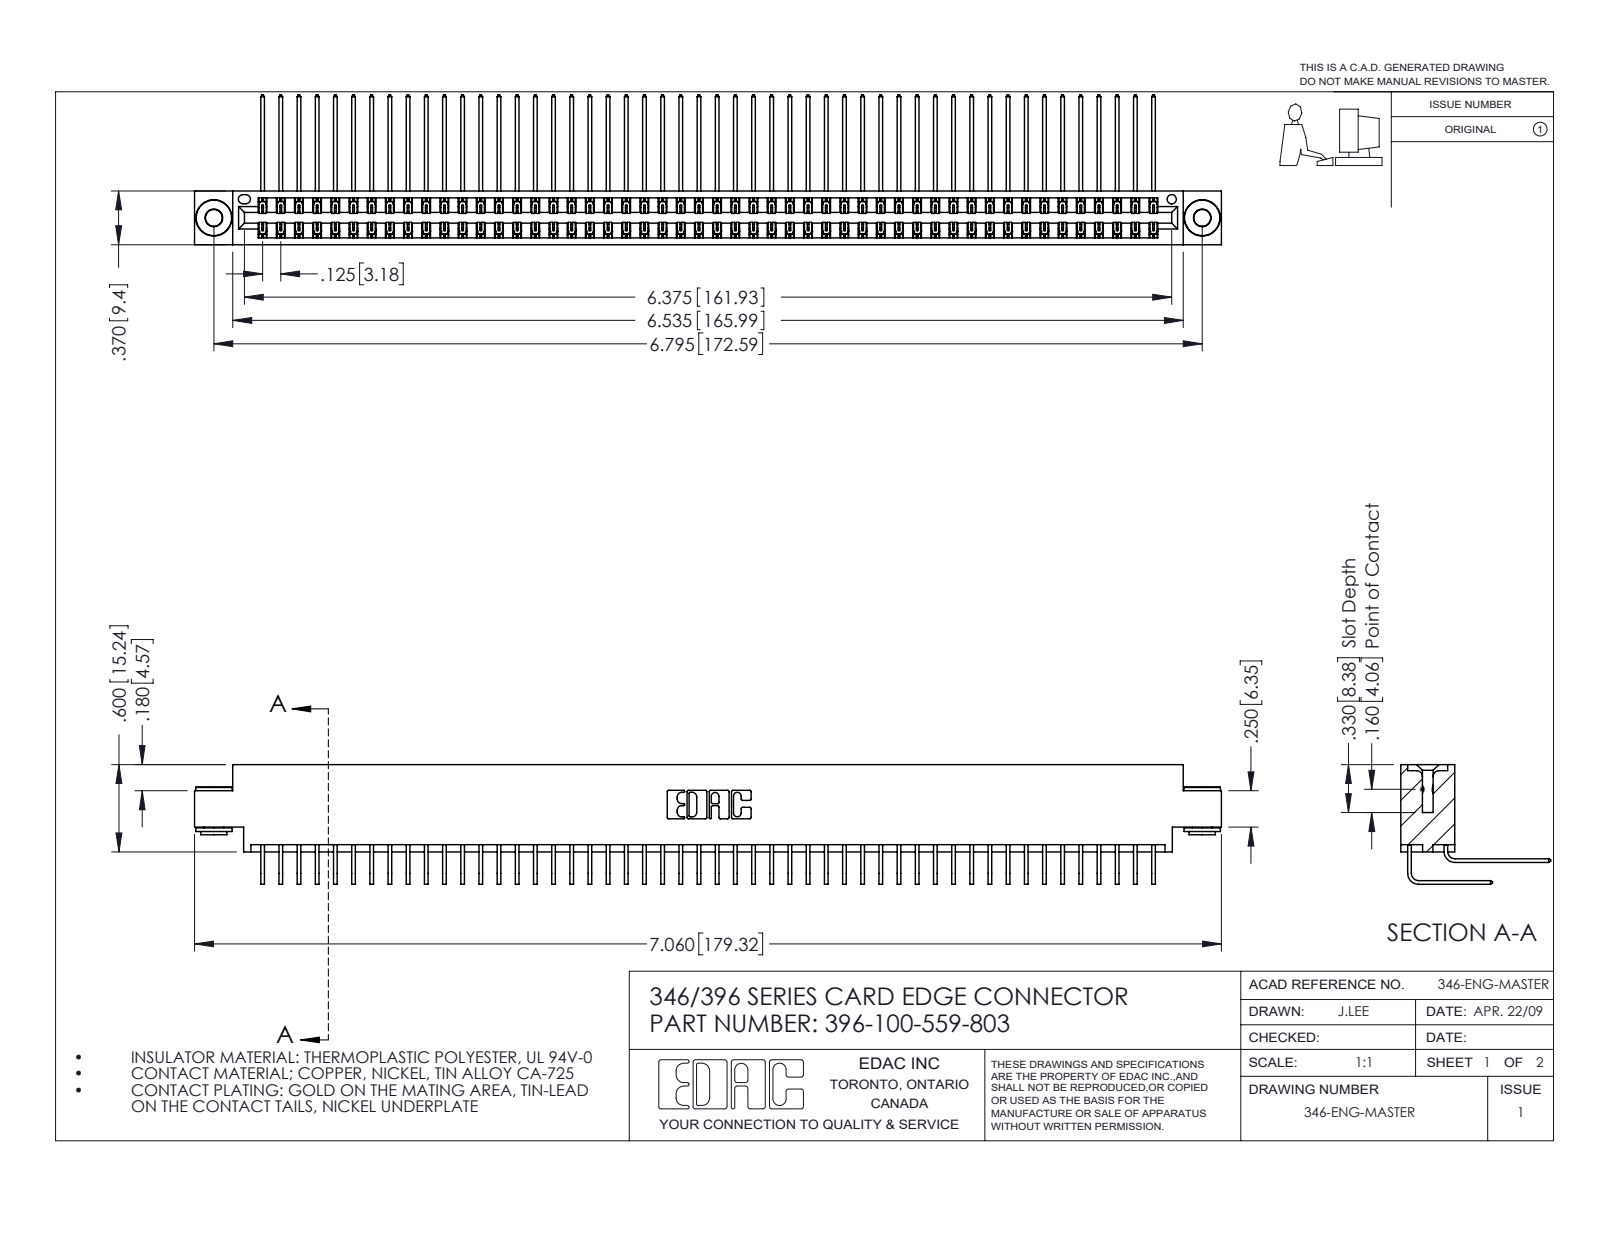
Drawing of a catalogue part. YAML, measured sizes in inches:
part_name: "345-292-001_559 Tail - 2; 396-100-559-803; 345-292-001_558 559 Tail - 1; 345-250-002_345-250-002-102 (+1 more)"
step_written_by: "SolidWorks 2016 (CONFIG_CONTROL_DESIGN)"
units: inches
bodies: {solids: 103, faces: 5564, planar: 3790, cylindrical: 1766, other: 8}
overall_size: [7.06, 1.03, 0.823]
volume: 1.098
surface_area: 43.42
round_holes:
  - {diameter: 0.116, count: 2}
  - {diameter: 0.156, count: 2}
  - {diameter: 0.064, count: 1}
round_bosses_or_shafts:
  - {diameter: 0.25, count: 2}
  - {diameter: 0.18, count: 2}
  - {diameter: 0.136, count: 2}
partial_cylinders:
  - {radius: 0.006, count: 150}
  - {radius: 0.01, count: 22}
  - {radius: 0.007, count: 6}
  - {radius: 0.031, count: 6}
  - {radius: 0.026, count: 3}
  - {radius: 0.014, count: 2}
  - {radius: 0.022, count: 2}
  - {radius: 0.024, count: 2}
face_to_face_distances: [0.048, 0.322, 0.025, 0.37, 0.25, 0.072, 0.298, 0.275, 0.148, 0.222]
hole_center_spacings: [0.246, 6.586, 6.795]
